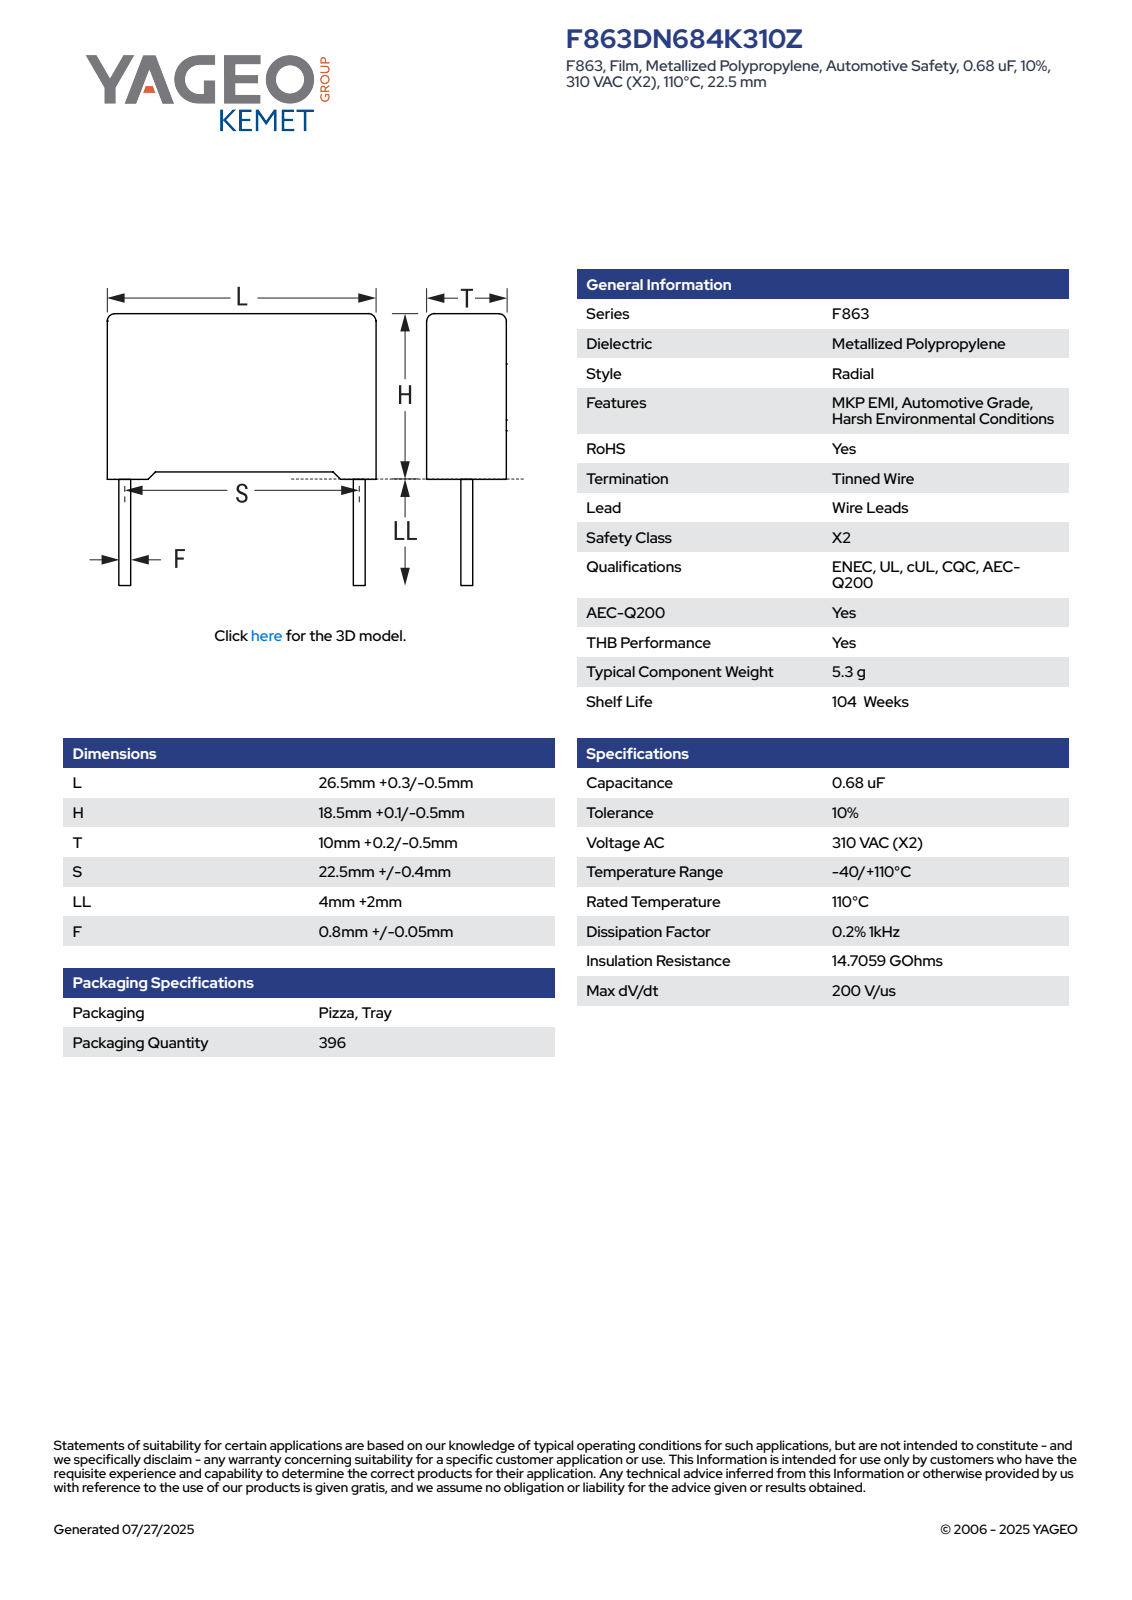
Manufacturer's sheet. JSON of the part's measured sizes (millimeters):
{"part_name": "CFR_RB_26.5X18.5X10_L26.8H18.6T10.2S22.5LL6F0.85", "step_written_by": "SolidWorks 2014 (AUTOMOTIVE_DESIGN)", "units": "millimeters", "bodies": {"solids": 4, "faces": 89, "planar": 81, "cylindrical": 8, "other": 0}, "overall_size": [26.8, 24.6, 10.21], "volume_mm3": 4864, "surface_area_mm2": 1955, "round_bosses_or_shafts": [[0.85, 2]], "partial_cylinders_radius": [[0.67, 4]], "face_to_face_distances": [10.2, 17.76, 26.8, 0.6, 9.6, 0.84, 18.6, 9, 14.82, 6]}
